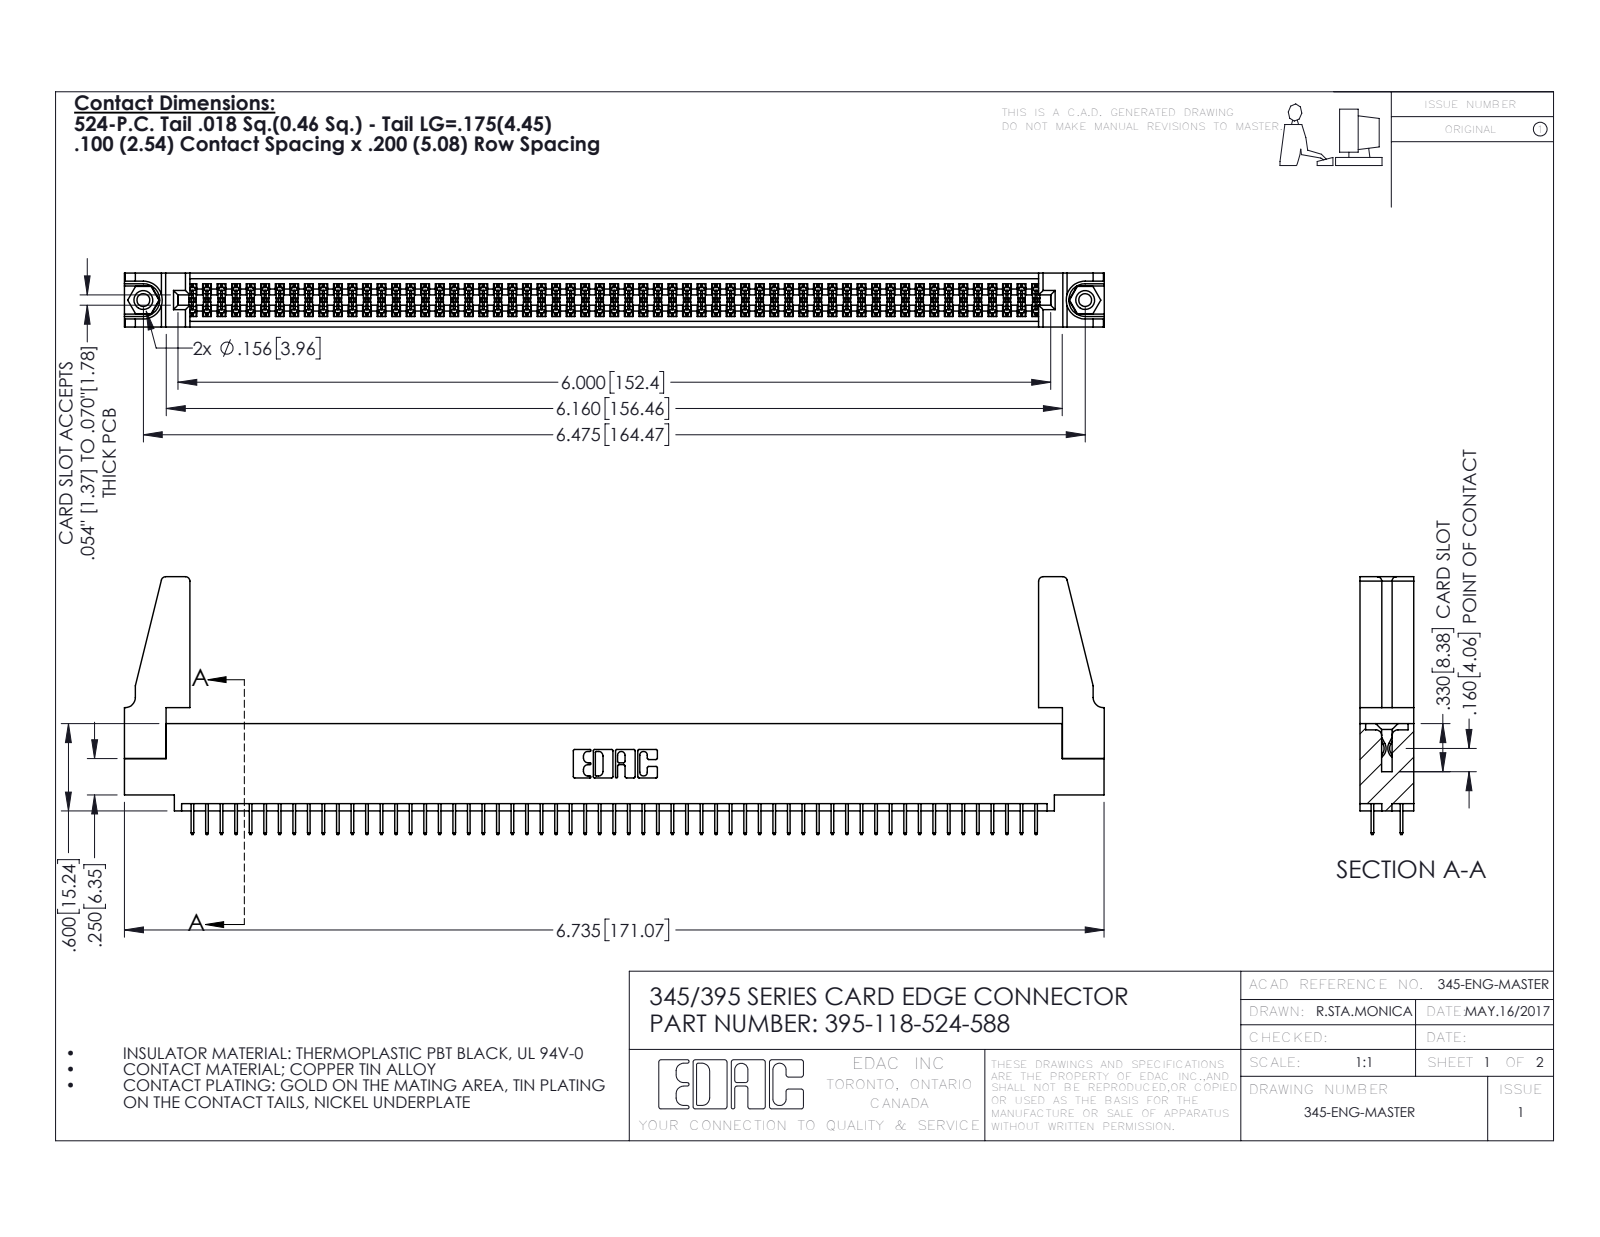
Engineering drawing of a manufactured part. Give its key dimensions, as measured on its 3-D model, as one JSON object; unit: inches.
{"part_name": "395-118-524-588; 345-220-078_345-220-088; 345-292-001_345-293-124; 345-250-001_345-250-001-102 (+1 more)", "step_written_by": "SolidWorks 2016 (CONFIG_CONTROL_DESIGN)", "units": "inches", "bodies": {"solids": 123, "faces": 6626, "planar": 4758, "cylindrical": 1852, "other": 16}, "overall_size": [6.736, 1.772, 0.37], "volume_in3": 1.207, "surface_area_in2": 42.63, "round_holes": [[0.089, 2], [0.125, 2], [0.156, 2], [0.064, 1]], "round_bosses_or_shafts": [[0.155, 2]], "partial_cylinders_radius": [[0.006, 177], [0.01, 22], [0.03, 8], [0.007, 6], [0.031, 6], [0.026, 3], [0.014, 2], [0.019, 2]], "face_to_face_distances": [0.072, 0.298, 0.37, 0.2, 0.098, 0.272, 0.025, 0.225, 0.072, 0.175], "hole_center_spacings": [0.27, 6.239, 6.475]}
